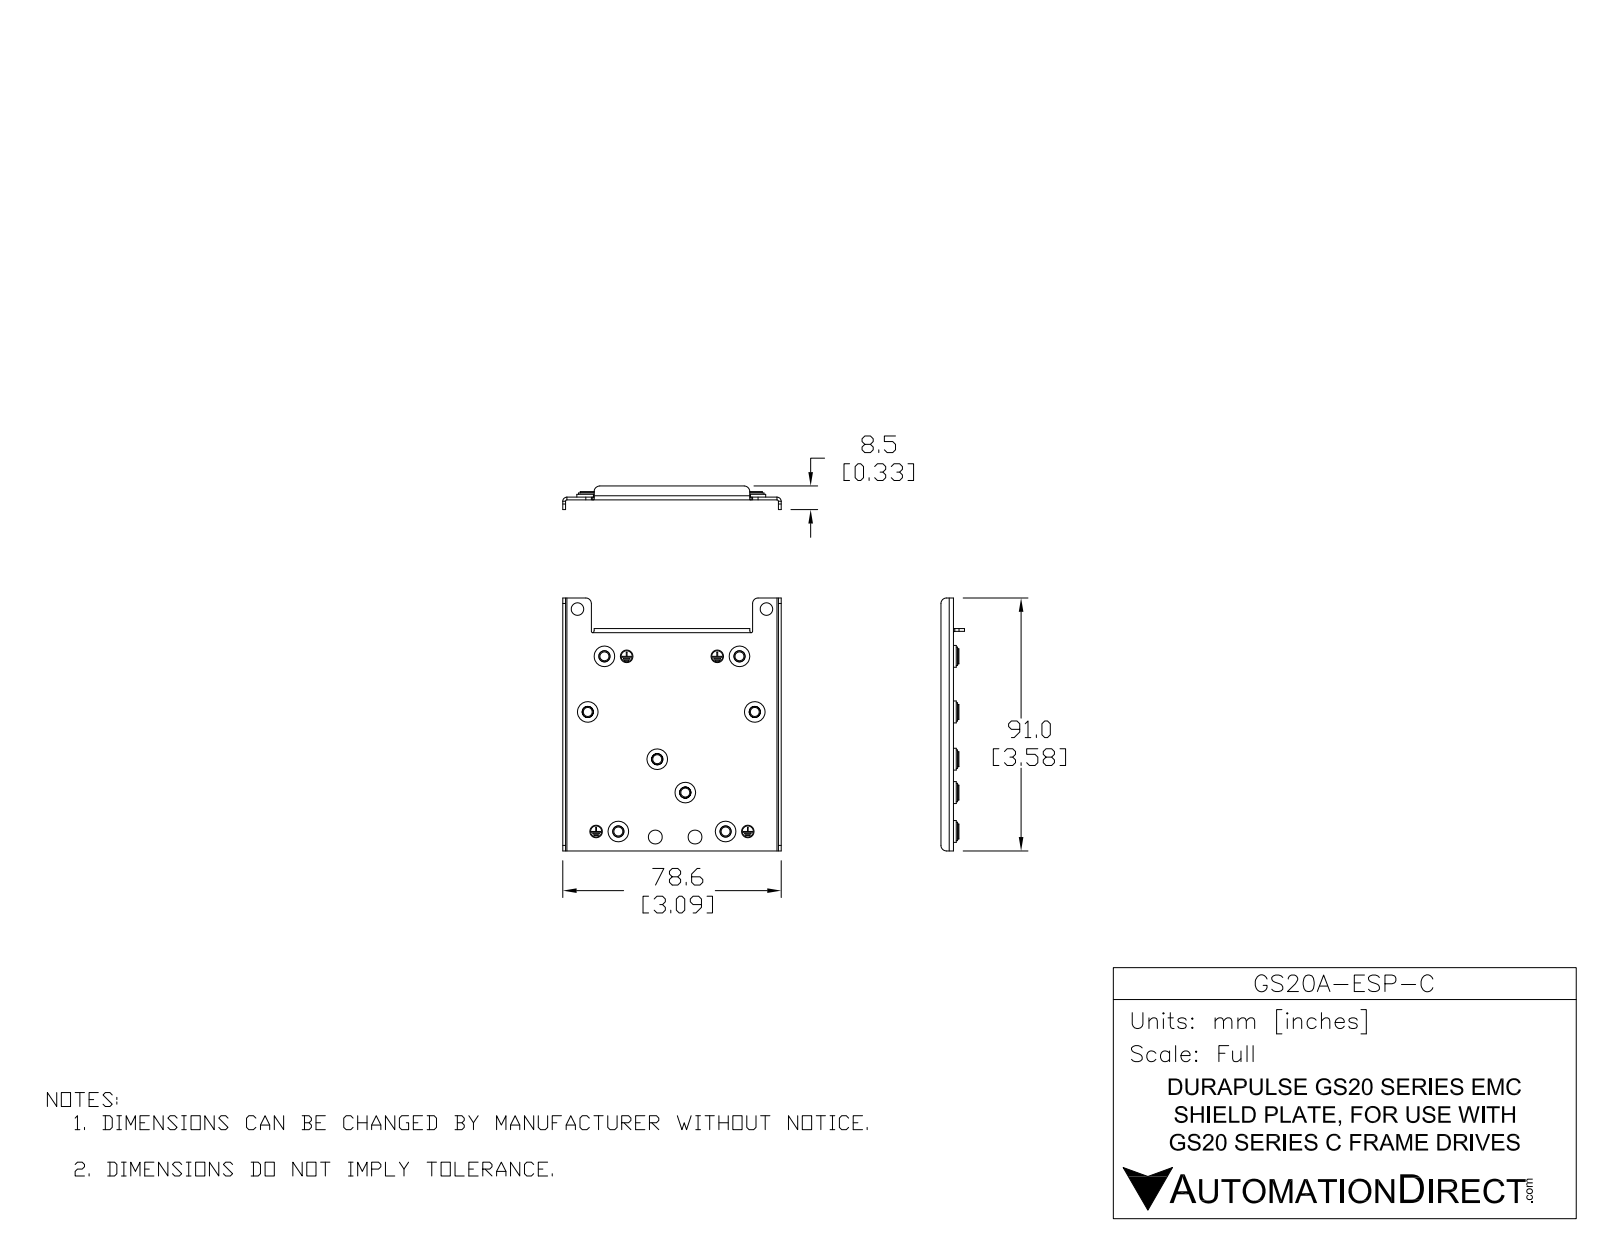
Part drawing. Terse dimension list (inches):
name: GS20A-ESP-C b
written by: SolidWorks 2017 (AUTOMOTIVE_DESIGN)
unit: in
bodies: 15 solids, 667 faces (271 planar, 172 cylindrical, 224 other)
size: 3.583 × 3.071 × 1.146
volume: 0.961 in³; area: 40.37 in²
holes: 8× ⌀0.128, 8× ⌀0.213, 4× ⌀0.213, 4× ⌀0.315, 2× ⌀0.177, 2× ⌀0.197
bosses: 8× ⌀0.31, 8× ⌀0.212, 5× ⌀0.261, 4× ⌀0.283, 3× ⌀0.261, 2× ⌀0.315, 2× ⌀0.272, 2× ⌀0.157
rounds: 12× R0.079, 8× R0.106, 8× R0.295, 6× R0.02, 3× R0.274, 3× R0.313, 2× R0.083, 1× R0.199
face distances: 0.063, 0.039, 0.102, 0.02, 0.719, 0.083, 0.079, 0.591, 0.758, 0.679
hole spacings: 0.354, 2.485, 3.003, 2.819, 0.776, 1.004, 1.341, 1.535
